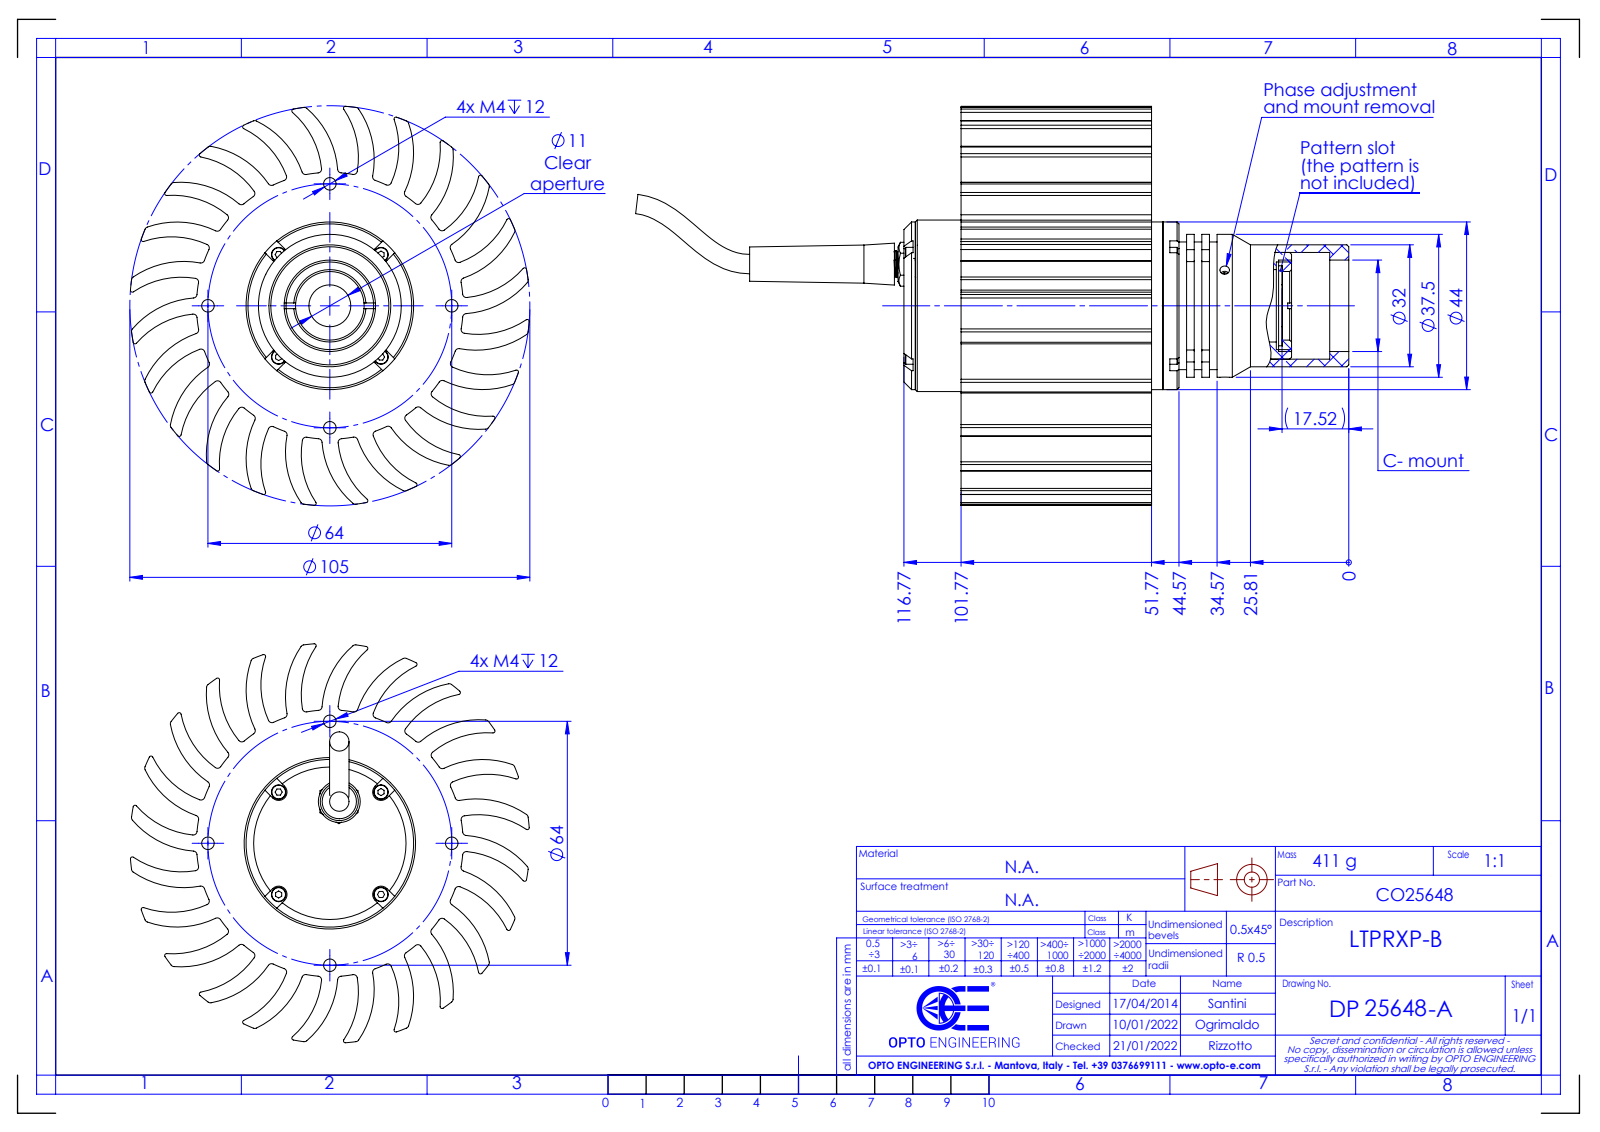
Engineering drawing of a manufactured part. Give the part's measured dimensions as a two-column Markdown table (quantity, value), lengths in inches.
| quantity | value |
| --- | --- |
| part name | DP25648-A_LTPRXP-B |
| STEP written by | SolidWorks 2021 (CONFIG_CONTROL_DESIGN) |
| units | inches |
| bodies | 0 solids, 480 faces (102 planar, 314 cylindrical, 64 other) |
| overall size | 7.37 × 4.121 × 4.121 |
| round holes (diameter × count) | 0.13 × 4, 0.098 × 3, 0.945 × 1, 1.102 × 1 |
| round bosses / shafts (diameter × count) | 0.15 × 4, 1.772 × 1, 1.732 × 1, 1.476 × 1, 1.319 × 1, 1.26 × 1 |
| partial cylindrical surfaces (radius × count) | 0.039 × 72, 0.02 × 24, 0.889 × 24, 0.925 × 24, 0.087 × 4, 0.089 × 4, 1.378 × 1, 2.067 × 1 |
| main face-to-face distances | 1.969, 2.559, 0.118, 0.591, 2.677, 2.087, 0.079, 0.472, 2.441, 0.157 |
| hole center spacings | 1.26, 1.781, 2.52 |
